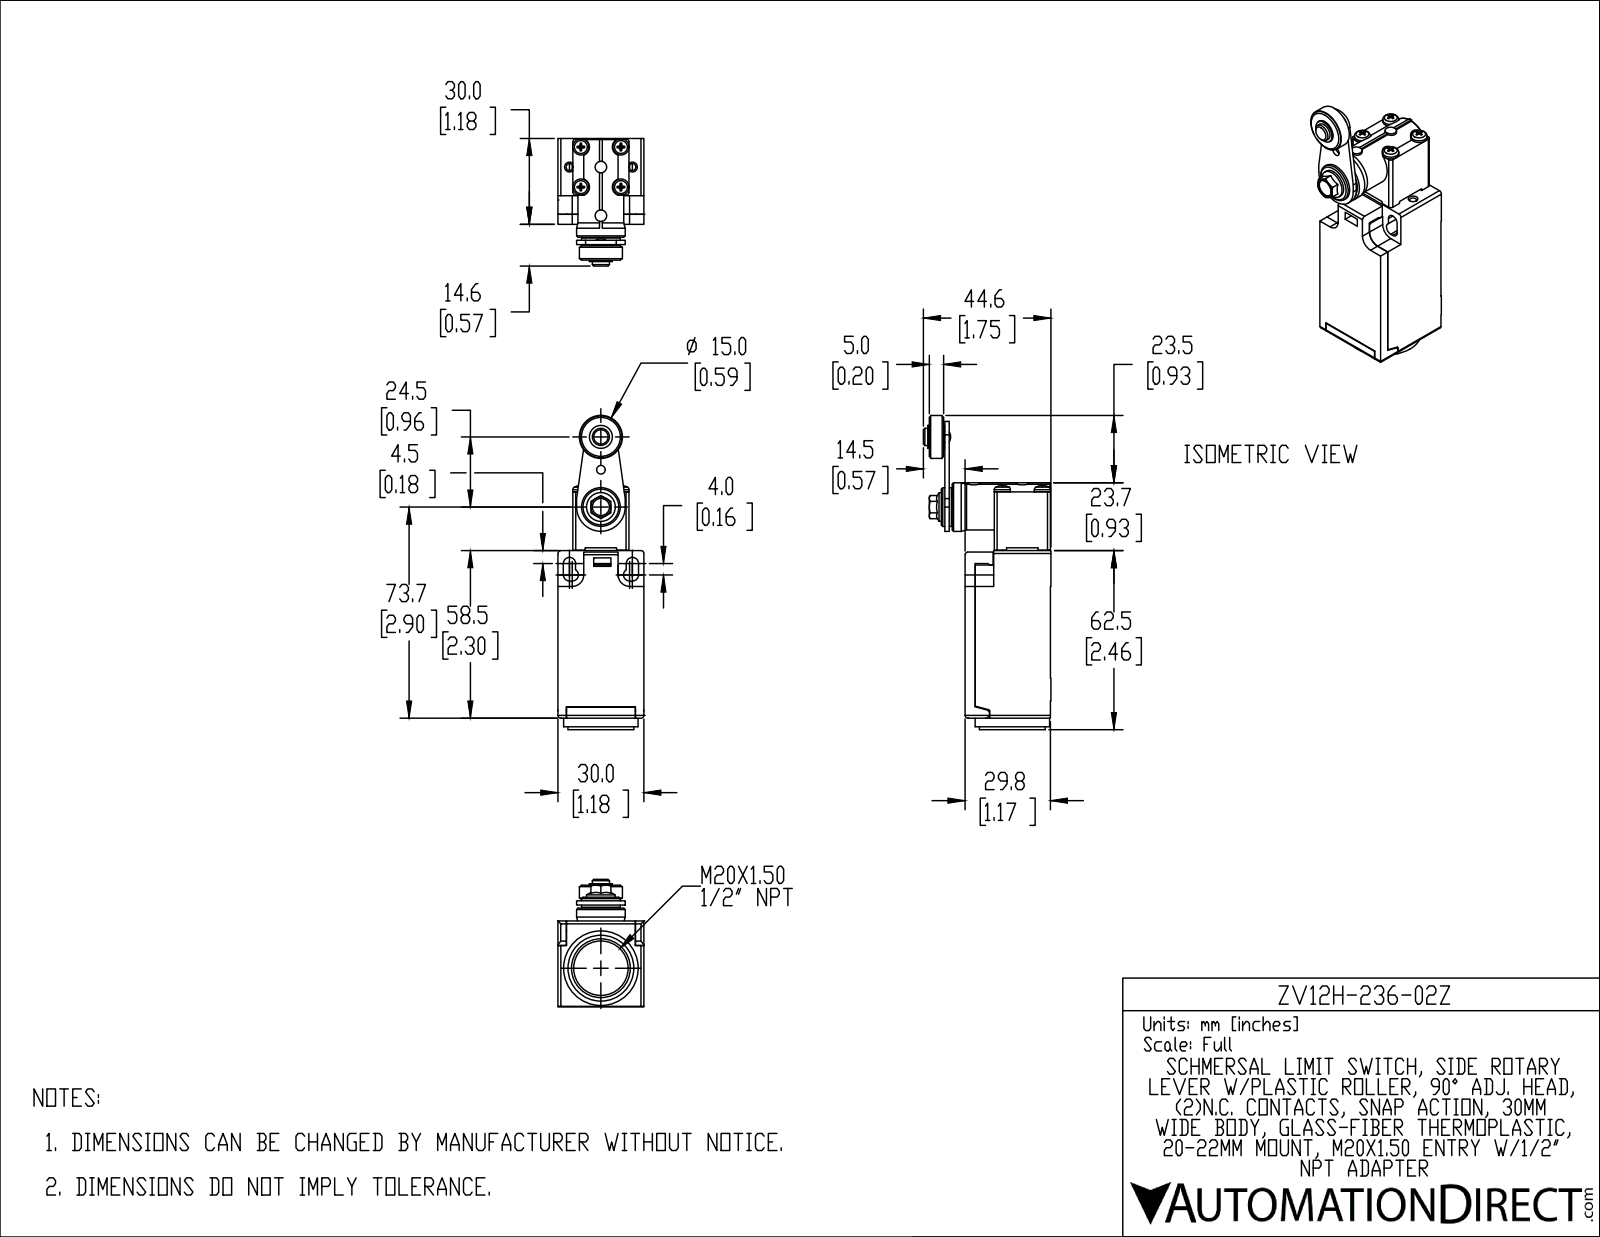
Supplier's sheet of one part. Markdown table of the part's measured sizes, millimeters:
| quantity | value |
| --- | --- |
| part name | ZV12H-236-02Z |
| STEP written by | SolidWorks 2019 (AUTOMOTIVE_DESIGN) |
| units | millimeters |
| bodies | 2 solids, 348 faces (237 planar, 84 cylindrical, 27 other) |
| overall size | 109.7 × 44.6 × 30 |
| volume | 60 850 mm³ |
| surface area | 19 440 mm² |
| round holes (diameter × count) | 2.4 × 6, 3.2 × 4, 3 × 1, 6 × 1, 13 × 1, 13.8 × 1, 19 × 1 |
| round bosses / shafts (diameter × count) | 5.6 × 4, 5.4 × 4, 4 × 3, 26 × 1, 23 × 1, 17 × 1, 16 × 1, 15 × 1 |
| partial cylindrical surfaces (radius × count) | 1 × 10, 2.2 × 6, 1.5 × 5, 3 × 4, 4 × 2, 0.2 × 1, 0.6 × 1, 5.4 × 1 |
| main face-to-face distances | 30, 26.3, 3.5, 29.8, 5.2, 24.8, 26.5, 19.6, 6, 4 |
| hole center spacings | 8.1, 9.9, 14, 19.3, 7.8, 11, 11.5, 12.6 |
